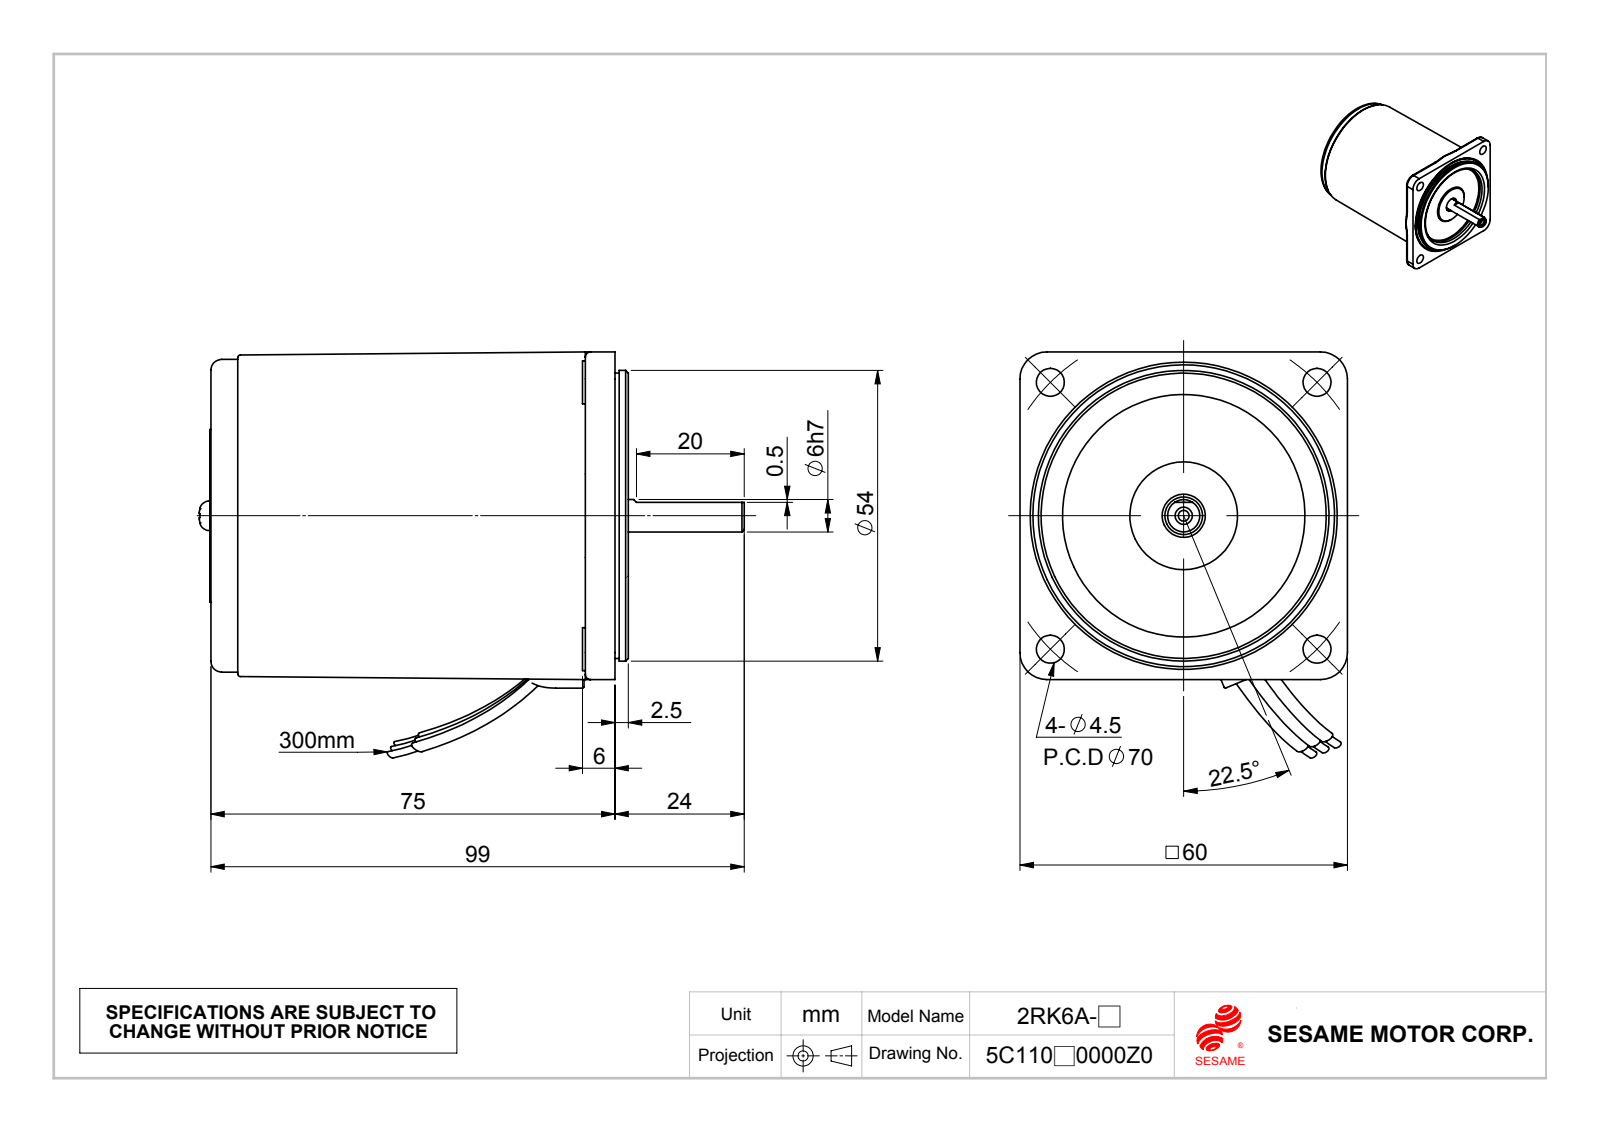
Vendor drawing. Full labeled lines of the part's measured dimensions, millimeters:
Part name (STEP PRODUCT): M206-RK_Default; 펥짰웰찿M2즤32x1t_Default; C254_Default; 06A_0成品 (+1 more)
STEP written by: SolidWorks 2010 (CONFIG_CONTROL_DESIGN)
Units: millimetres
Bodies: 10 solids, 293 faces (100 planar, 100 cylindrical, 93 other)
Overall size (bounding box): 101.16 × 75.35 × 60.8
Volume: 219 095 mm³ · Surface area: 32 143 mm²
Round holes (diameter × count): ⌀5.2 ×4, ⌀2.5 ×3, ⌀4 ×2, ⌀2 ×1, ⌀7 ×1, ⌀7.2 ×1, ⌀9.5 ×1, ⌀32.2 ×1, ⌀45 ×1, ⌀56 ×1
Round bosses / shafts (diameter × count): ⌀8 ×4, ⌀5.5 ×2, ⌀3 ×2, ⌀58 ×1, ⌀53.93 ×1, ⌀52.93 ×1, ⌀32 ×1, ⌀9.3 ×1
Partial cylindrical surfaces — rounded edges, fillets, slot ends (radius × count): R0.25 ×8, R0.3 ×8, R1 ×4, R5 ×4, R5.25 ×1, R29 ×1
Main face-to-face distances: 1, 73.7, 1.5, 72.6, 72.7, 0.8, 74.2, 1.6, 75, 73.5
Hole centre spacings: 27.73, 35, 44.51, 49.5, 12.25, 70, 24.5
